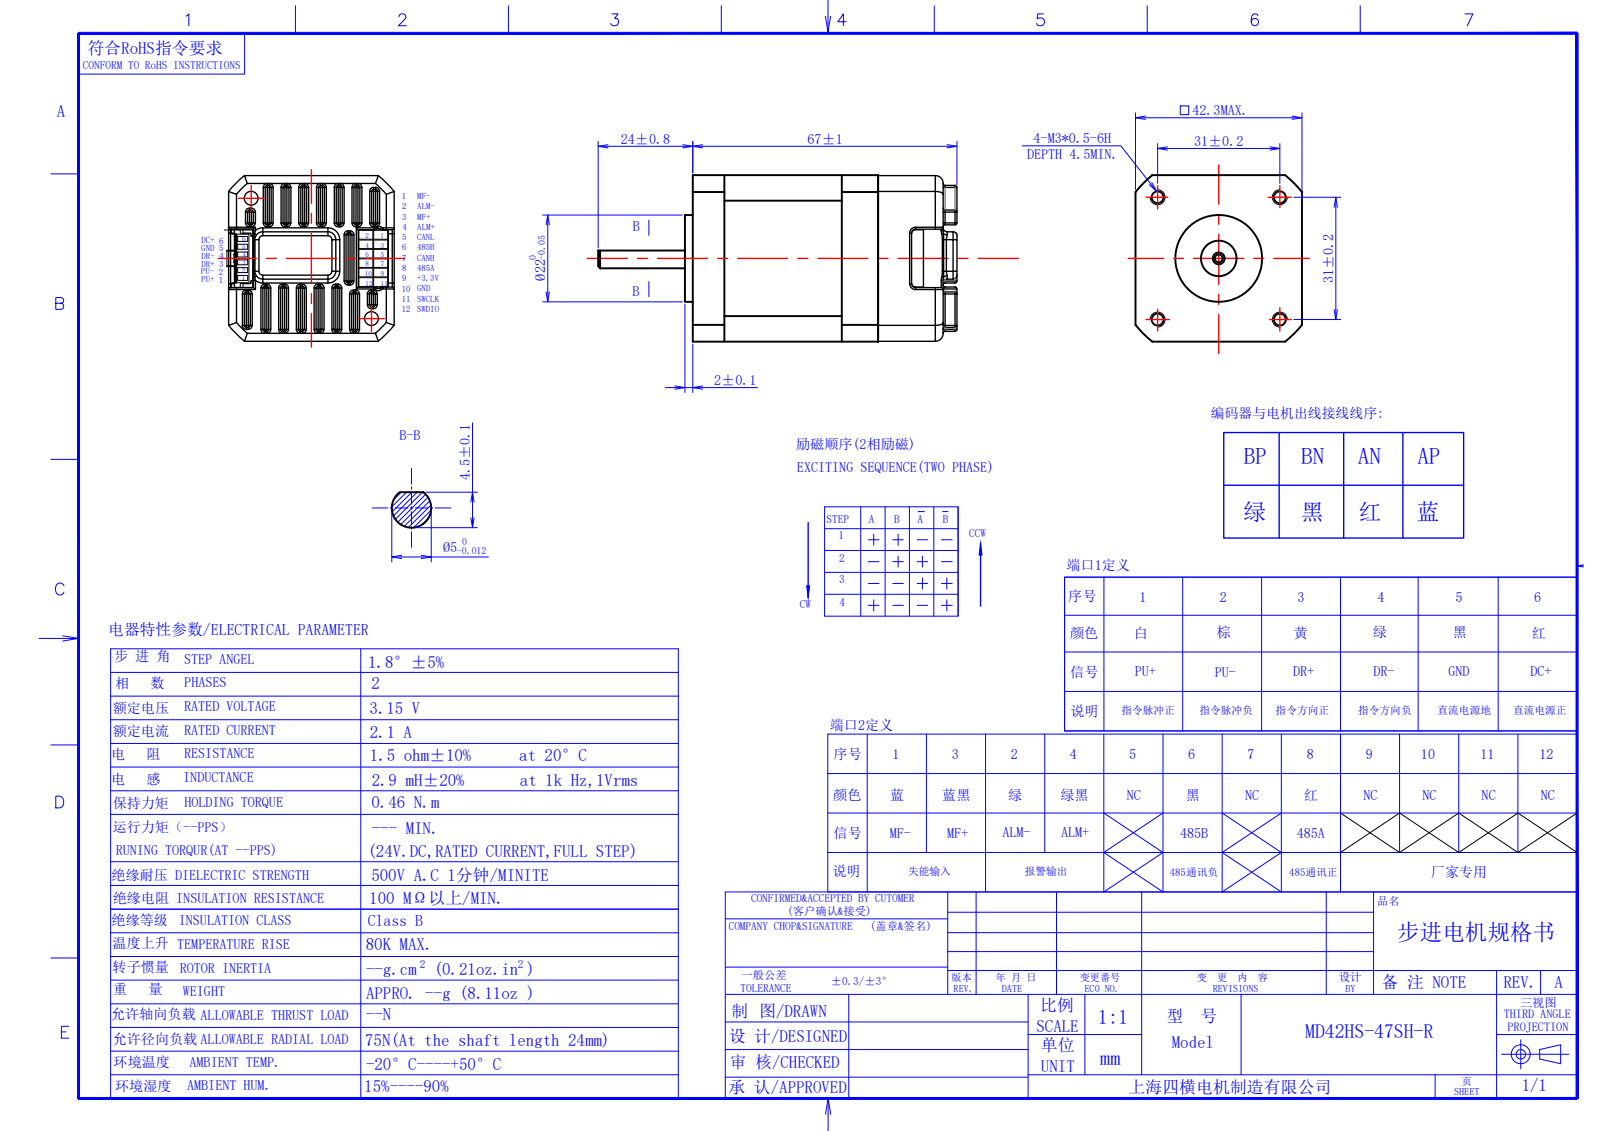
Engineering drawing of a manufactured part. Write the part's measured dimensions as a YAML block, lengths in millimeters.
part_name: "M3螺钉-L42mm; M3螺钉-L60mm; 353620650.stp; HX20028-12A.stp (+8 more)"
step_written_by: "SolidWorks 2022 (CONFIG_CONTROL_DESIGN)"
units: millimeters
bodies: {solids: 13, faces: 1758, planar: 932, cylindrical: 545, other: 281}
overall_size: [91, 42.3, 42.3]
volume: 87552
surface_area: 39910
round_holes:
  - {diameter: 2.5, count: 6}
  - {diameter: 3.3, count: 4}
  - {diameter: 3.5, count: 4}
  - {diameter: 5.5, count: 4}
  - {diameter: 1.05, count: 2}
  - {diameter: 1.5, count: 2}
  - {diameter: 1.75, count: 2}
  - {diameter: 3.1, count: 2}
  - {diameter: 4.5, count: 2}
  - {diameter: 2, count: 1}
  - {diameter: 6, count: 1}
  - {diameter: 9, count: 1}
round_bosses_or_shafts:
  - {diameter: 5, count: 5}
  - {diameter: 3, count: 4}
  - {diameter: 2.1, count: 2}
  - {diameter: 25.9, count: 1}
  - {diameter: 22, count: 1}
  - {diameter: 8, count: 1}
partial_cylinders:
  - {radius: 0.5, count: 174}
  - {radius: 1.5, count: 37}
  - {radius: 1, count: 24}
  - {radius: 0.41, count: 8}
  - {radius: 0.44, count: 8}
  - {radius: 2, count: 8}
  - {radius: 0.3, count: 4}
  - {radius: 0.85, count: 2}
face_to_face_distances: [47, 8, 42.3, 30, 39, 9, 1.5, 42.15, 17, 38]
hole_center_spacings: [30.75, 0.35, 1.41, 1.46, 17.11, 17.44, 17.92, 21.57]
